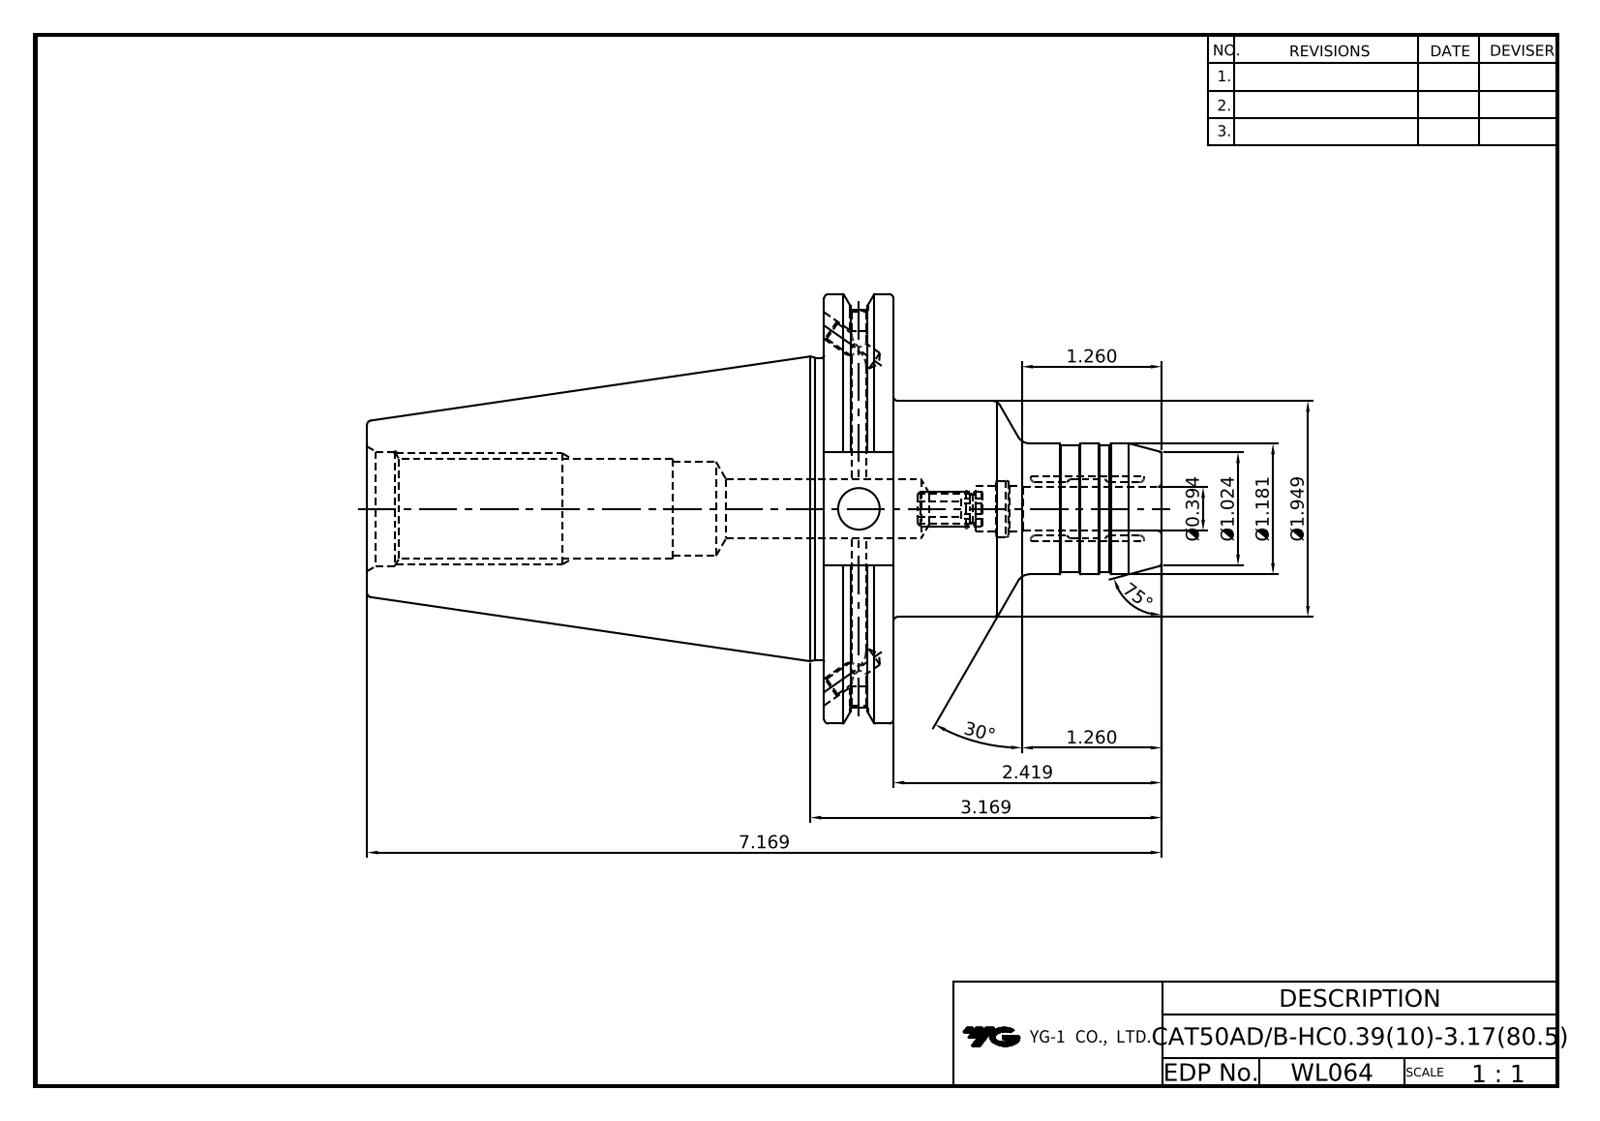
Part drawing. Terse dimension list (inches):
name: LO-CAT50ADB-HC10-80.5
written by: Autodesk Inventor 2022 (AUTOMOTIVE_DESIGN)
unit: in
bodies: 1 solid, 108 faces (37 planar, 33 cylindrical, 38 other)
size: 7.169 × 3.875 × 3.728
volume: 24.26 in³; area: 81.75 in²
holes: 2× ⌀0.128, 2× ⌀0.163, 2× ⌀0.165, 2× ⌀0.197, 1× ⌀0.272, 1× ⌀0.375, 1× ⌀0.394, 1× ⌀0.417, 1× ⌀0.531, 1× ⌀0.807, 1× ⌀0.865, 1× ⌀1.031
bosses: 1× ⌀3.875, 1× ⌀3.594, 1× ⌀2.726, 1× ⌀1.949, 1× ⌀1.181, 1× ⌀1.142
face distances: 0.625, 4.125, 4.75, 7.169, 3.044, 2.419, 2.875, 1.02, 4.363, 0.238
